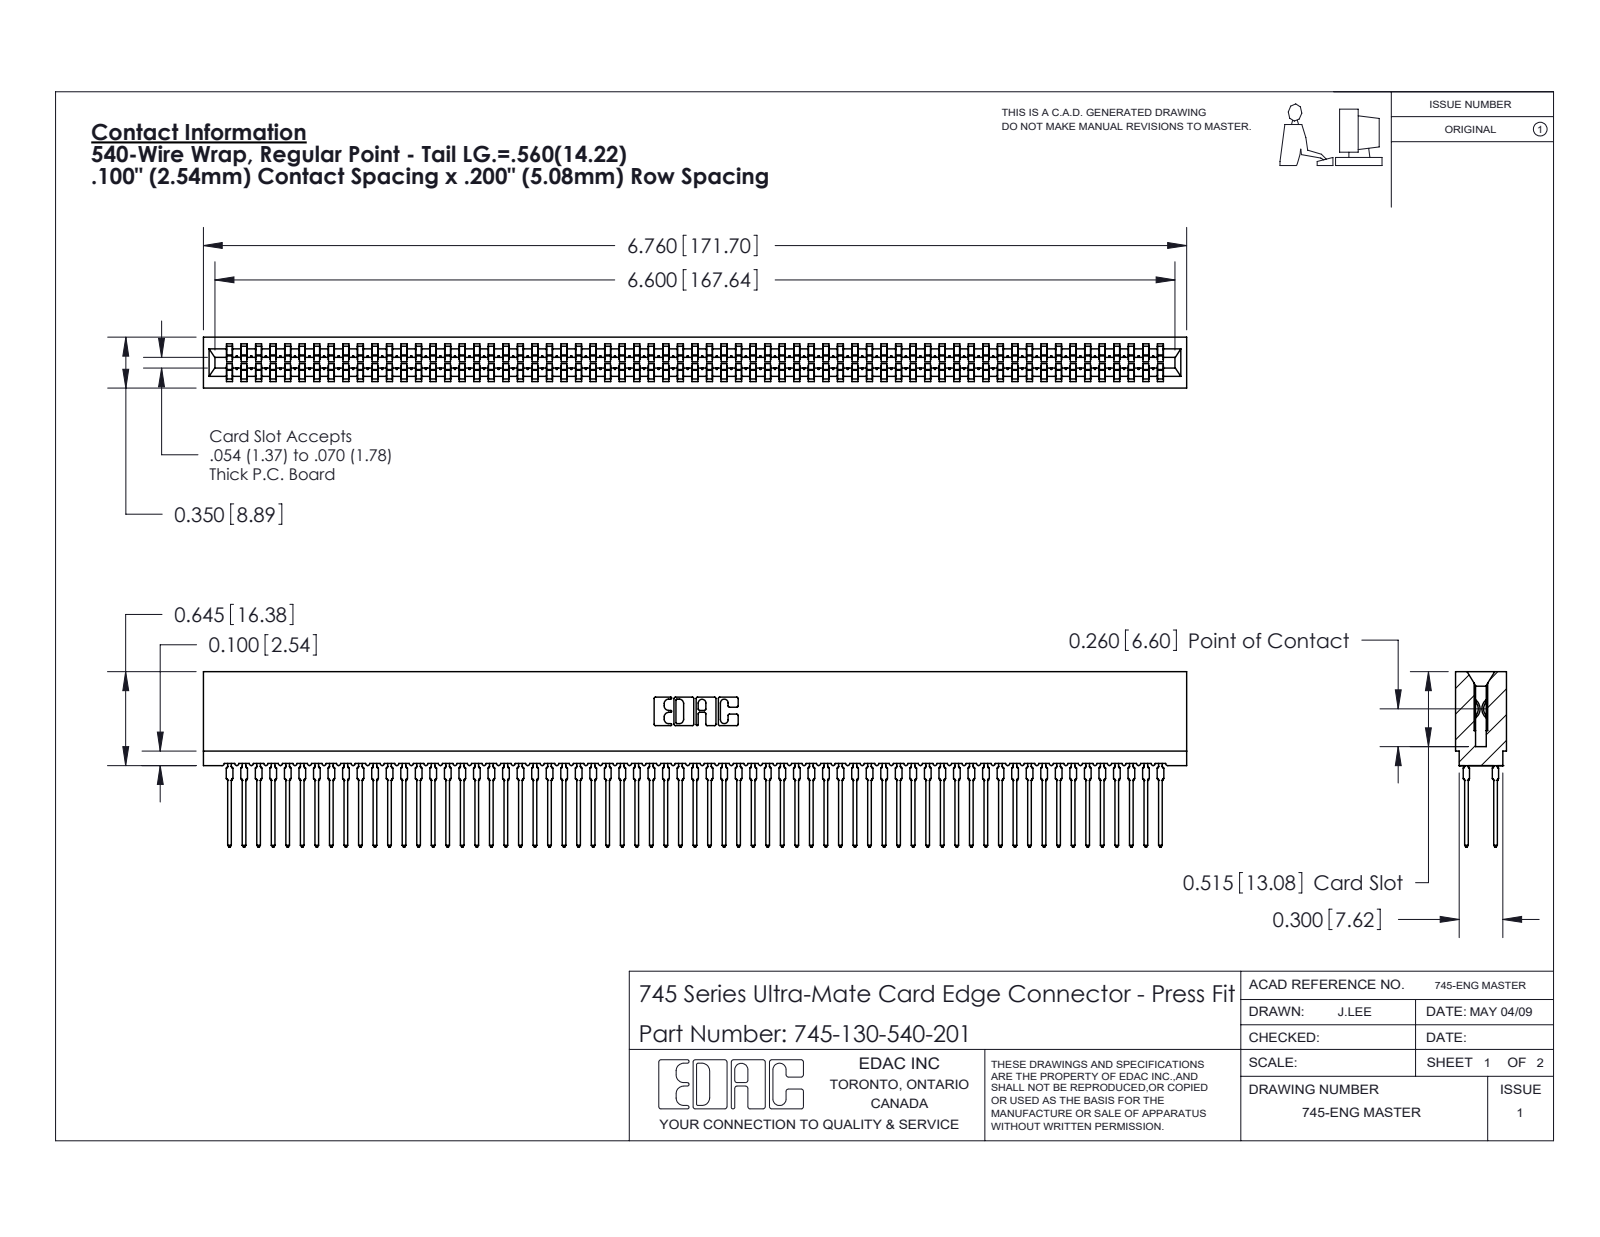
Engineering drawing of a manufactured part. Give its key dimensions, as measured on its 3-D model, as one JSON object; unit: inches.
{"part_name": "745-292-001_540; 745 Part_Insulator Option - 01; 745-130-540-201", "step_written_by": "SolidWorks 2020 (CONFIG_CONTROL_DESIGN)", "units": "inches", "bodies": {"solids": 131, "faces": 11730, "planar": 6035, "cylindrical": 2315, "other": 3380}, "overall_size": [6.76, 1.206, 0.35], "volume_in3": 0.959, "surface_area_in2": 52.65, "partial_cylinders_radius": [[0.021, 260], [0.015, 130], [0.01, 22], [0.005, 8], [0.011, 8], [0.007, 6], [0.031, 6], [0.026, 3]], "face_to_face_distances": [0.063, 0.287, 0.35, 0.2, 0.045, 0.305, 0.018, 0.243, 0.138, 0.212]}
